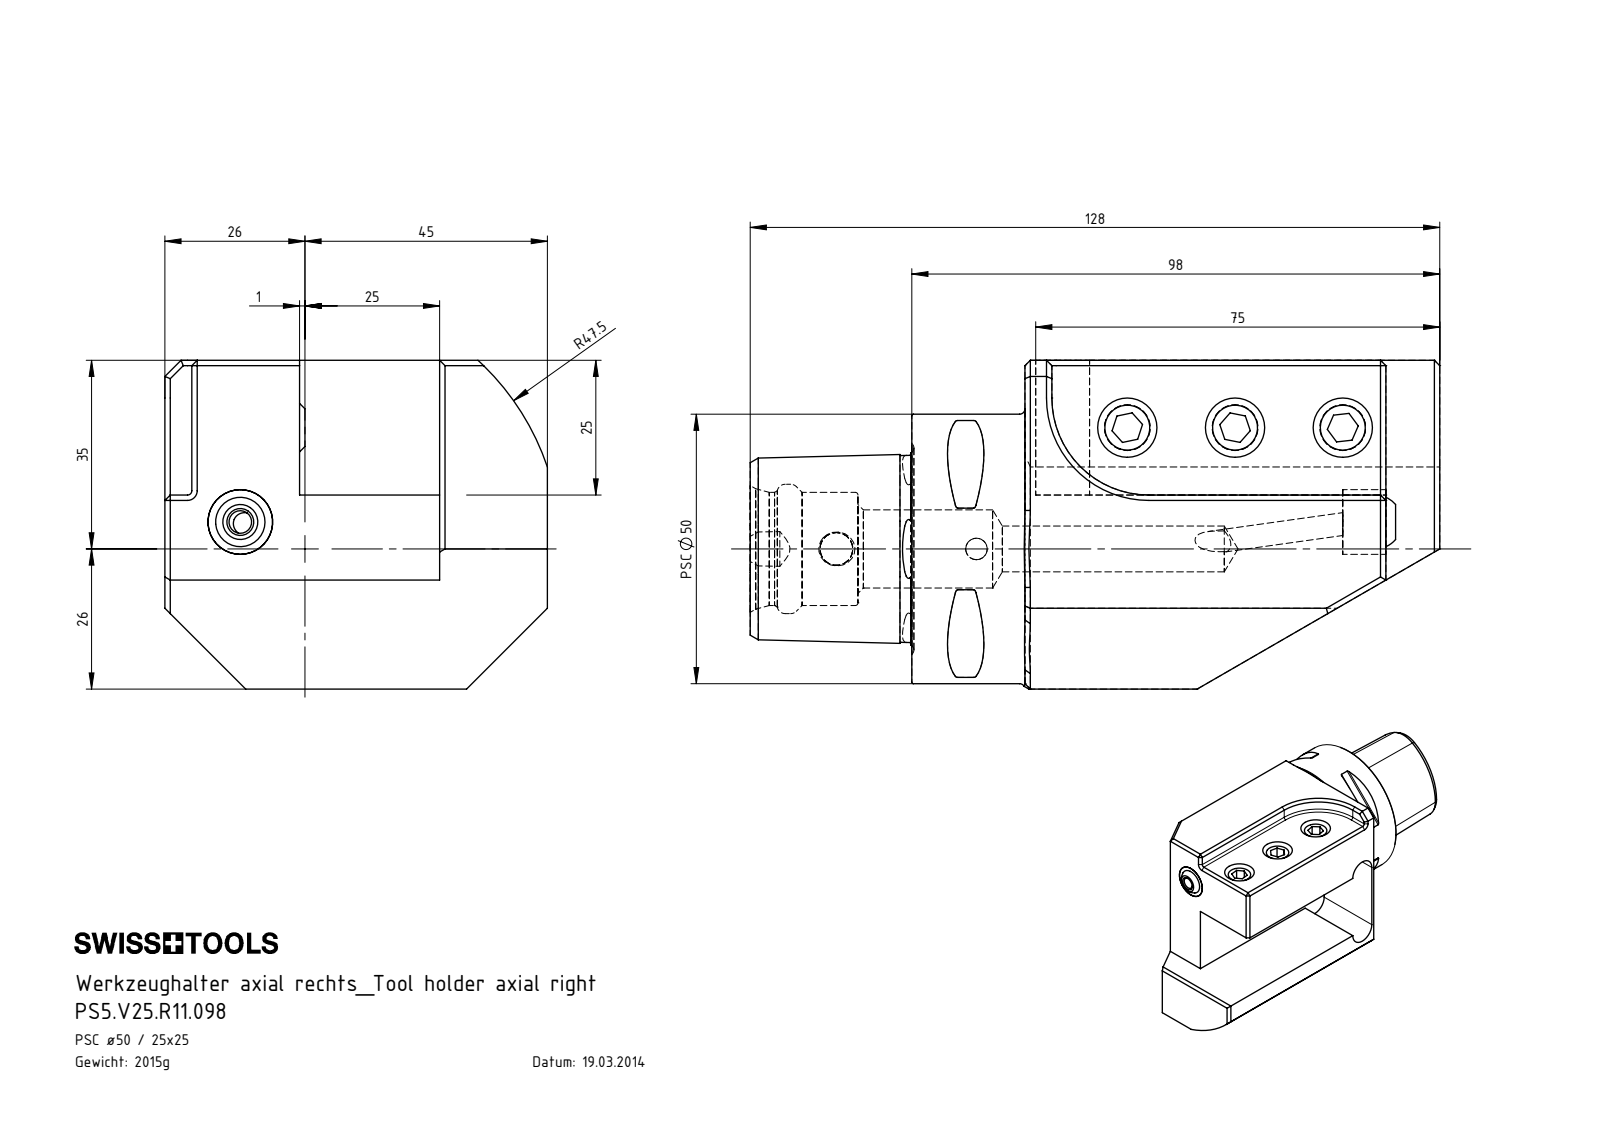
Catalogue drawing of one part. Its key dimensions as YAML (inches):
part_name: "PS5-V25.R11.098_A; KU1-U12.001.010; KU1-U12.001.010_2; PS5.V25.R11.098 (+2 more)"
step_written_by: "SolidWorks 2017 (AUTOMOTIVE_DESIGN)"
units: inches
bodies: {solids: 6, faces: 198, planar: 93, cylindrical: 35, other: 70}
overall_size: [5.039, 2.795, 2.402]
volume: 15.68
surface_area: 65.9
round_holes:
  - {diameter: 0.335, count: 4}
  - {diameter: 0.165, count: 2}
  - {diameter: 0.157, count: 1}
  - {diameter: 0.24, count: 1}
  - {diameter: 0.276, count: 1}
  - {diameter: 0.472, count: 1}
  - {diameter: 0.571, count: 1}
  - {diameter: 0.827, count: 1}
  - {diameter: 0.945, count: 1}
round_bosses_or_shafts:
  - {diameter: 0.394, count: 3}
  - {diameter: 1.969, count: 1}
partial_cylinders:
  - {radius: 0.02, count: 8}
  - {radius: 0.031, count: 2}
  - {radius: 0.197, count: 2}
  - {radius: 0.157, count: 1}
  - {radius: 0.709, count: 1}
  - {radius: 1.87, count: 1}
face_to_face_distances: [0.984, 0.787, 1.811, 2.008, 2.795, 1.024, 1.417, 2.402, 0.197, 2.638]
hole_center_spacings: [0.787, 0.512, 1.024, 1.414, 1.575, 2.087, 2.303, 2.82]
